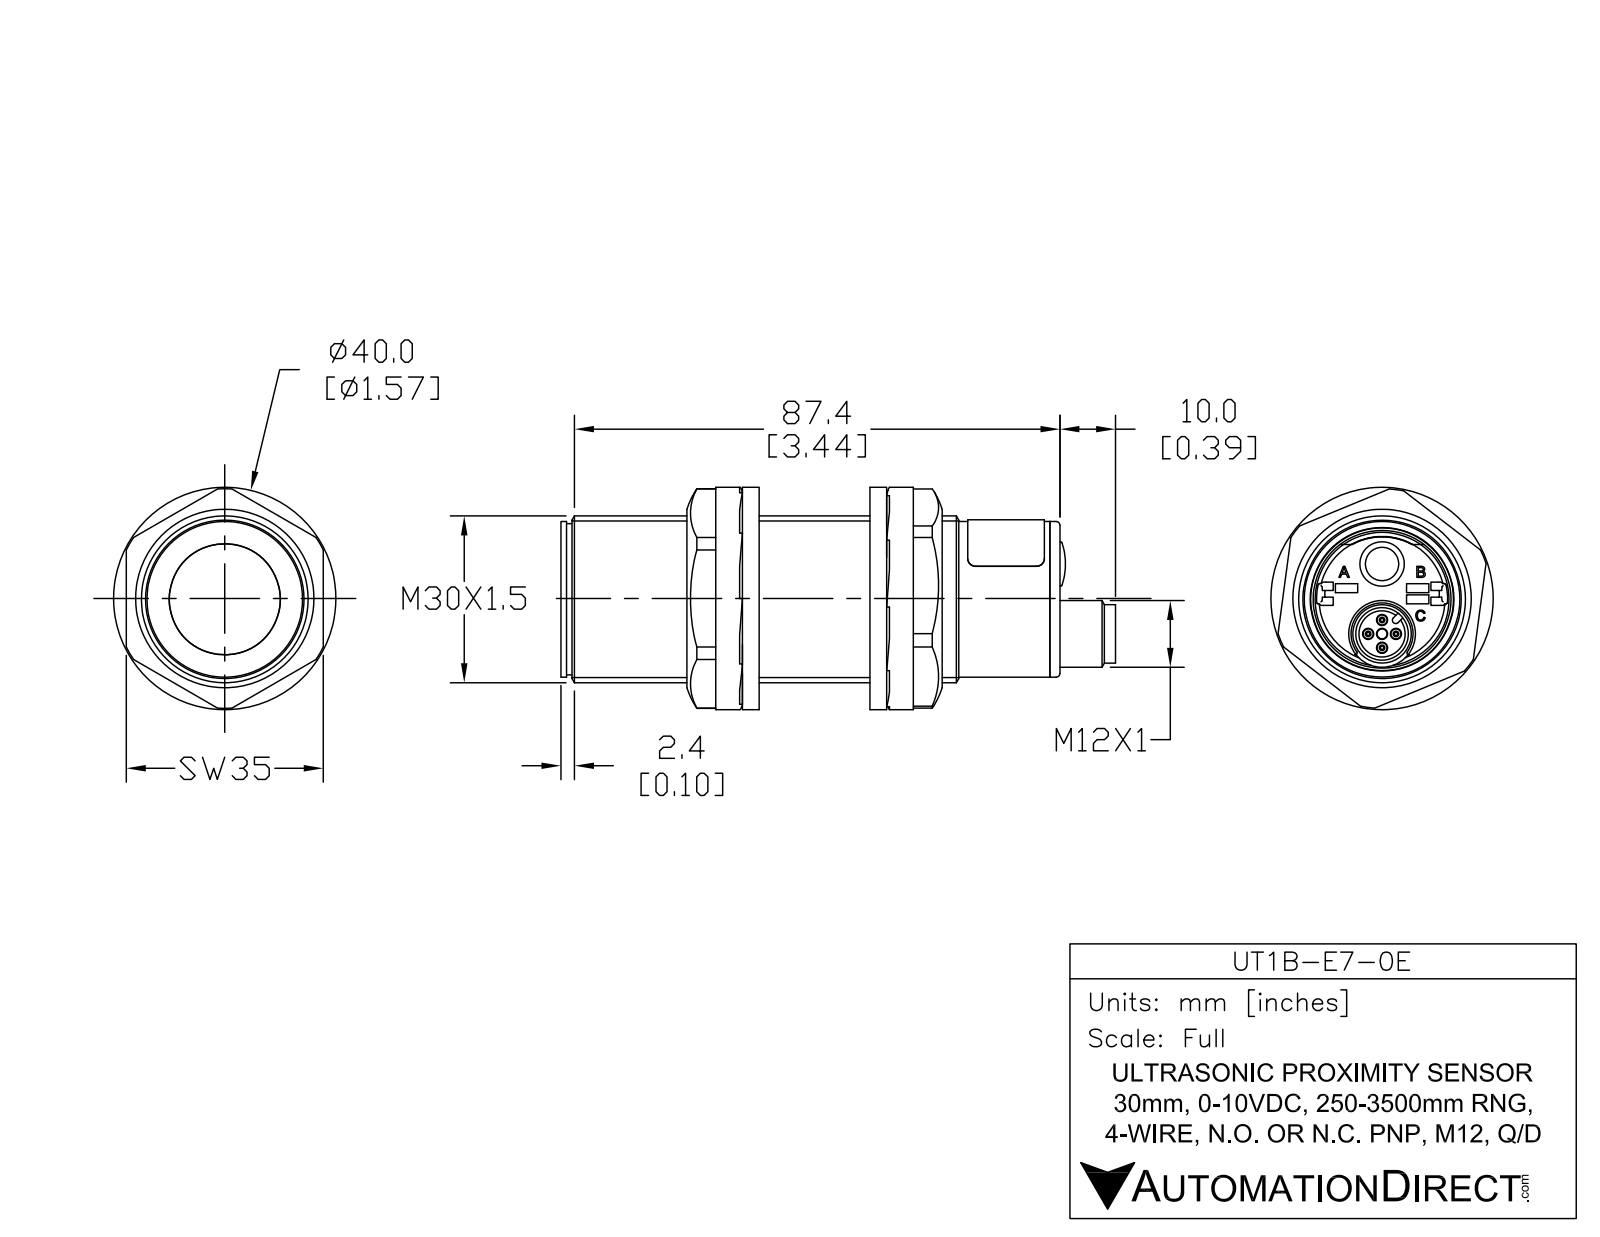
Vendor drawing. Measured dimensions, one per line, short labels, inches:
name: UT1B-E7-0E
written by: SolidWorks 2017 (AUTOMOTIVE_DESIGN)
unit: in
bodies: 5 solids, 107 faces (30 planar, 45 cylindrical, 32 other)
size: 3.89 × 1.181 × 1.181
volume: 3.754 in³; area: 20.71 in²
holes: 4× ⌀0.071, 1× ⌀0.315, 1× ⌀0.327, 1× ⌀0.372, 1× ⌀0.925
bosses: 4× ⌀0.039, 1× ⌀1.181, 1× ⌀1.102, 1× ⌀1.071, 1× ⌀0.472, 1× ⌀0.413, 1× ⌀0.364
rounds: 2× R0.012, 1× R0.024
face distances: 3.386, 3.457, 0.039, 3.425, 0.071, 3.496, 0.039, 0.059, 3.425, 3.496
hole spacings: 0.098, 0.139, 0.197, 0.264, 0.505, 0.146, 0.245, 0.25
